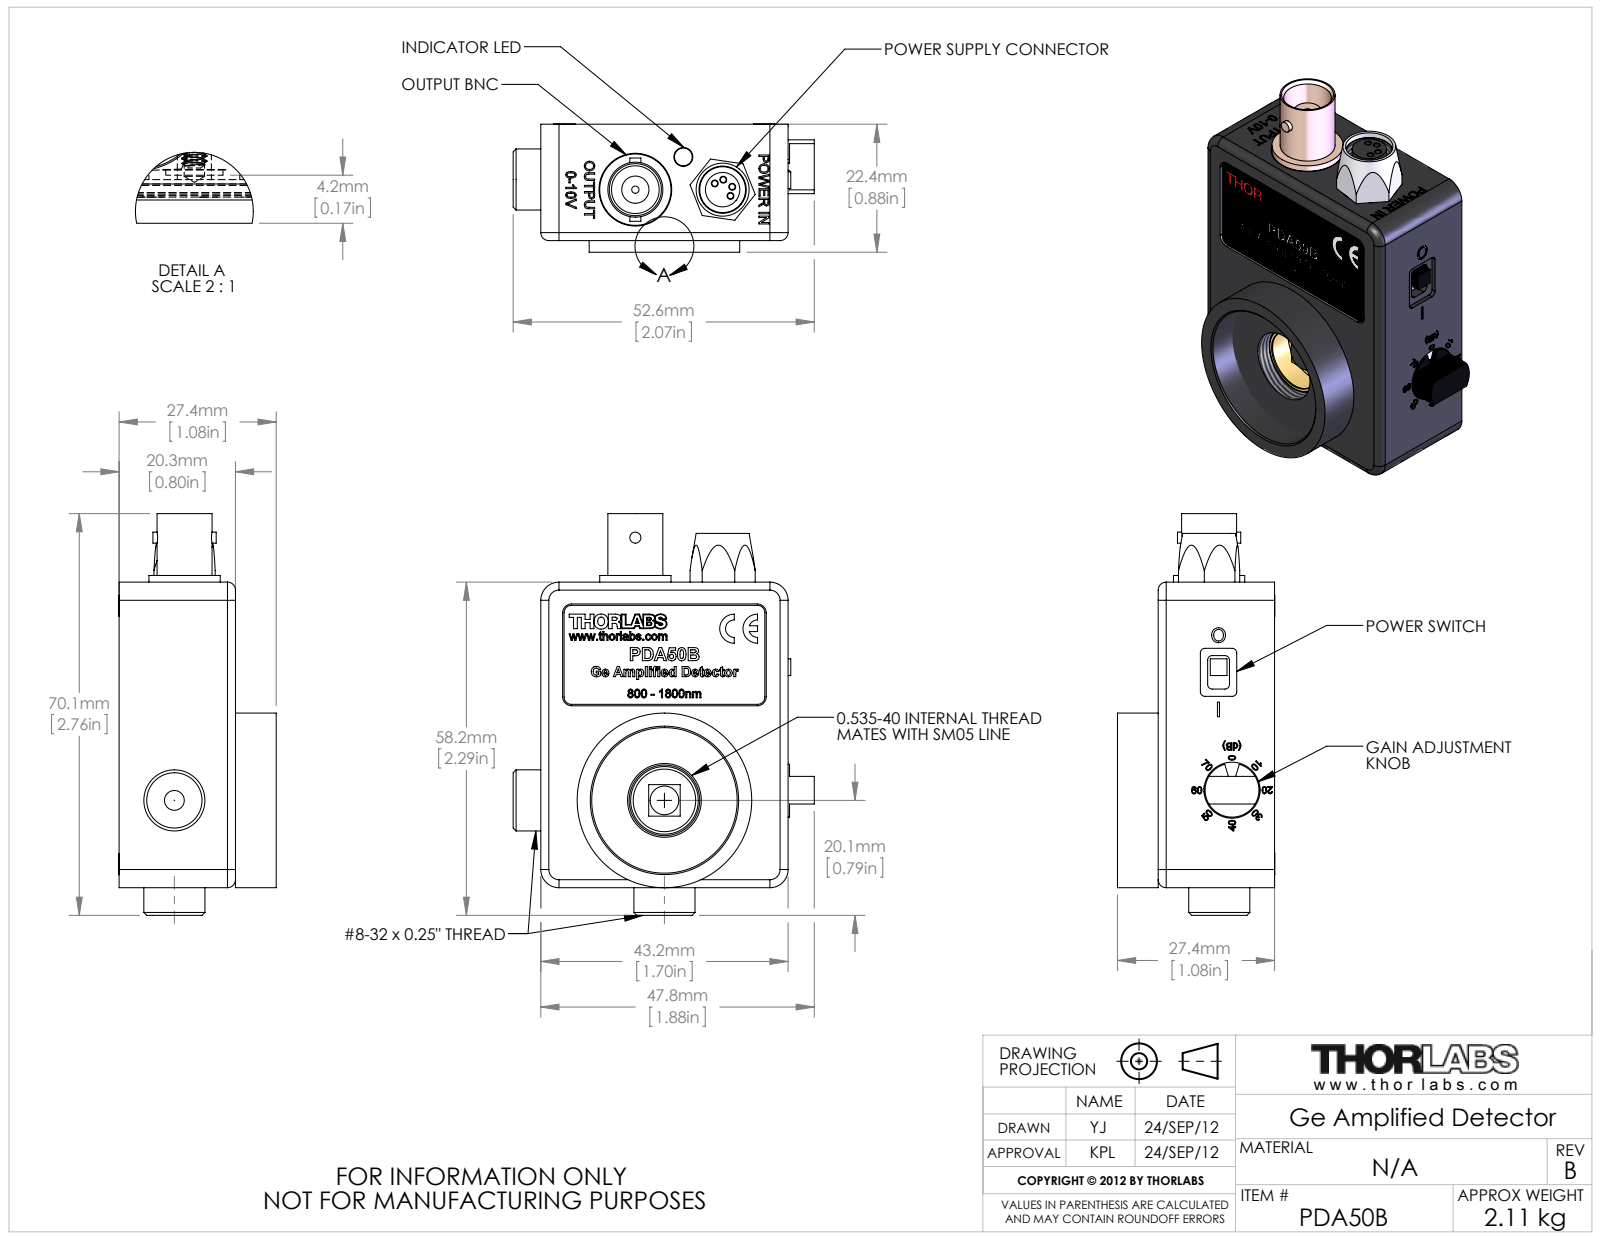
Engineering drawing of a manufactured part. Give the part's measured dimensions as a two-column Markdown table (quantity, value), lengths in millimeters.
| quantity | value |
| --- | --- |
| part name | 13125-E0W |
| STEP written by | SolidWorks 2011 (AUTOMOTIVE_DESIGN) |
| units | millimeters |
| bodies | 56 solids, 4209 faces (2475 planar, 861 cylindrical, 873 other) |
| overall size | 70.12 × 52.58 × 27.47 |
| volume | 24 613 mm³ |
| surface area | 28 569 mm² |
| round holes (diameter × count) | 0.94 × 9, 0.81 × 8, 1.78 × 7, 2.44 × 6, 0.2 × 5, 0.76 × 4, 1 × 4, 3.17 × 4, 5.08 × 4, 1.27 × 3, 3.45 × 2, 3.81 × 2 |
| round bosses / shafts (diameter × count) | 3.73 × 4, 2.18 × 4, 10.67 × 2, 9.4 × 2, 5.99 × 2, 0.45 × 2, 30.48 × 1, 26.29 × 1 |
| partial cylindrical surfaces (radius × count) | 0.2 × 46, 0.1 × 36, 3.17 × 23, 0.25 × 10, 0.35 × 8, 0.79 × 8, 2.41 × 8, 1.27 × 5 |
| main face-to-face distances | 1.59, 2.54, 12.76, 14.35, 1.58, 12.77, 1.78, 11.18, 1.27, 0.51 |
| hole center spacings | 2.54, 2, 3.2, 3.25, 3.59, 5.08, 5.15, 7.11 |
